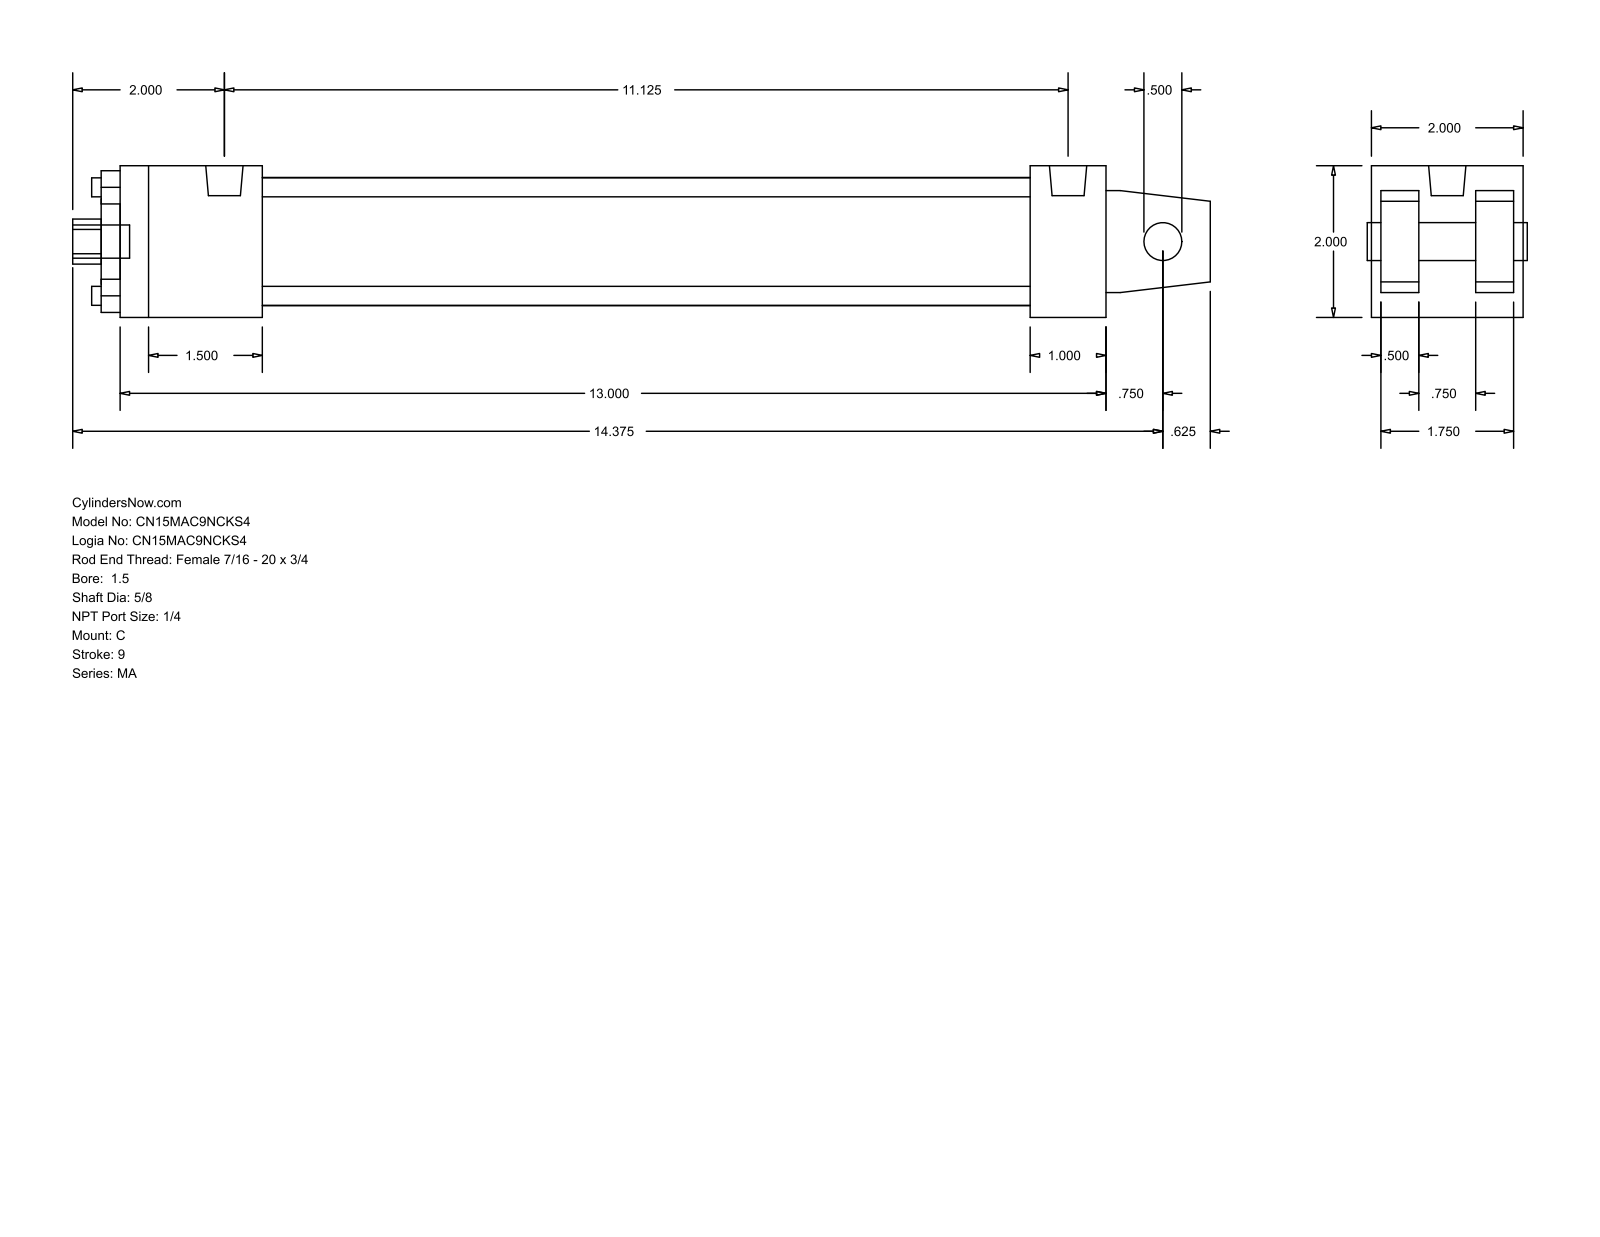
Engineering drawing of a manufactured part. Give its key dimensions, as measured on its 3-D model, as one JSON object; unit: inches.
{"part_name": "MA_C__0150_0.625", "step_written_by": "GSSL Pune (CONFIG_CONTROL_DESIGN)", "units": "inches", "bodies": {"solids": 0, "faces": 103, "planar": 76, "cylindrical": 27, "other": 0}, "overall_size": [15, 2, 2], "round_holes": [[0.25, 4], [0.5, 1], [0.625, 1], [1.125, 1], [1.69, 1]], "round_bosses_or_shafts": [[0.313, 4], [0.492, 2], [0.437, 1]], "partial_cylinders_radius": [[0.297, 1]], "face_to_face_distances": [2, 1.375, 0.5, 0.125, 0.625, 1.875, 1.25, 13, 12, 1], "hole_center_spacings": [1.011, 1.43, 2.022]}
